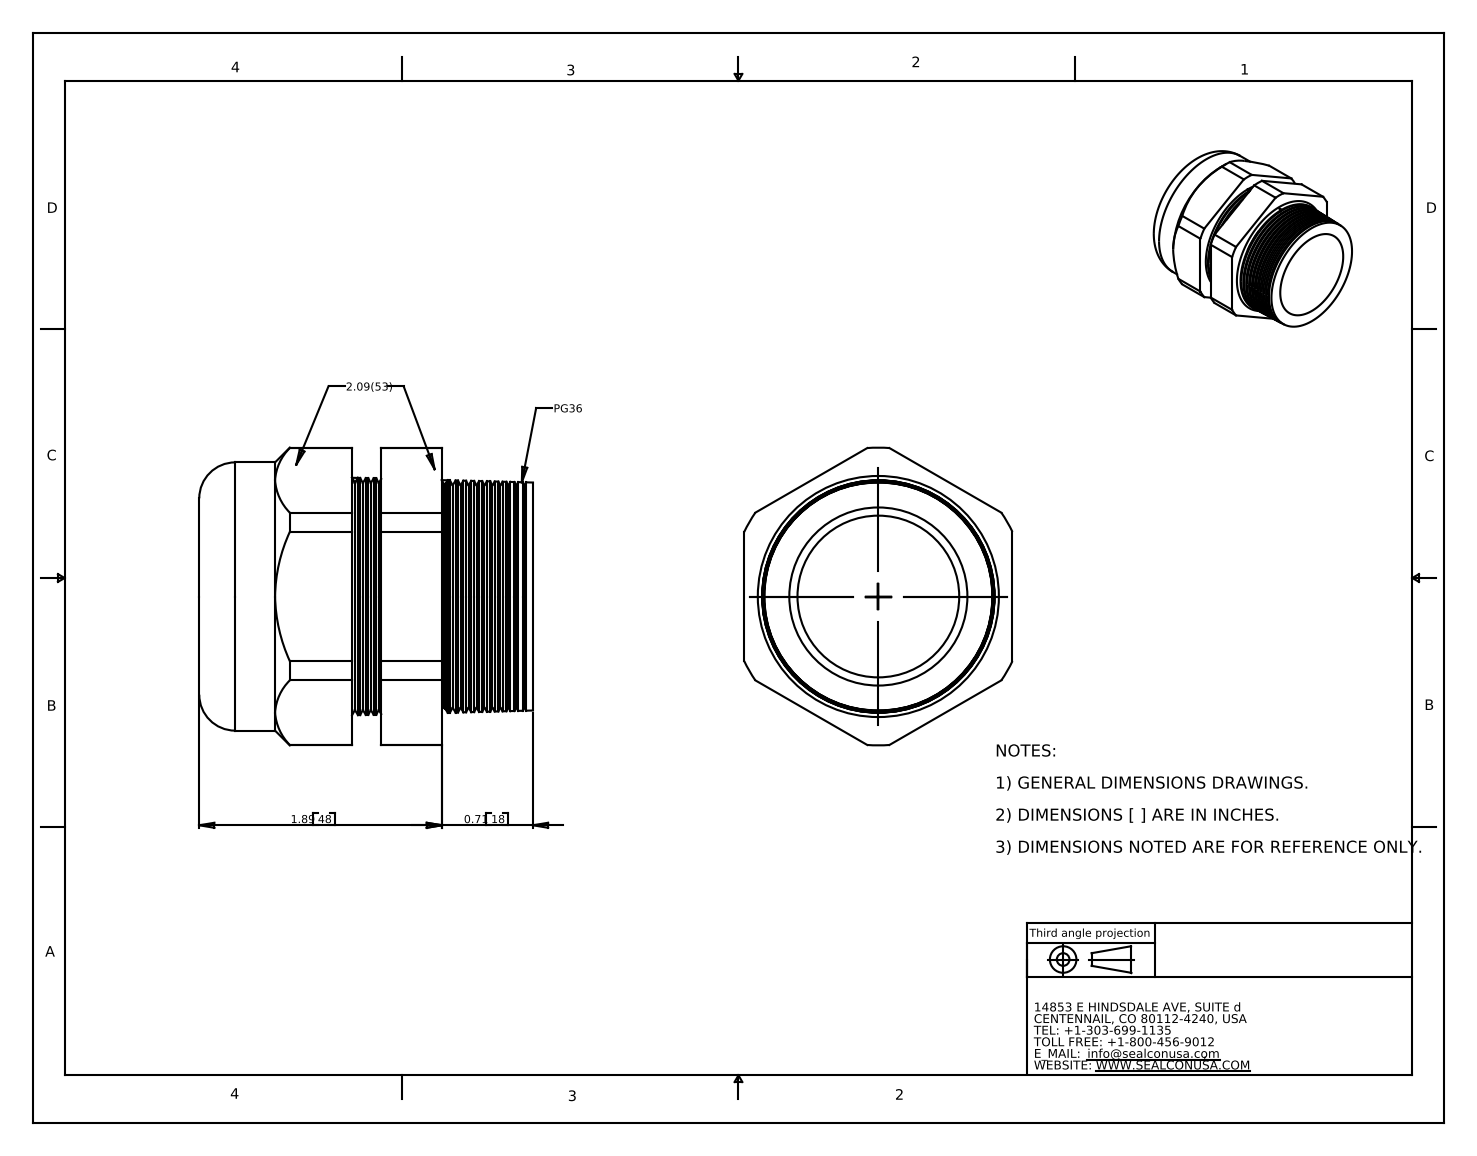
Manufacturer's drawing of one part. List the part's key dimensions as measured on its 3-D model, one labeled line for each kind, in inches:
Part name (STEP PRODUCT): CD36CA-BK
STEP written by: SolidWorks 2007 (CONFIG_CONTROL_DESIGN)
Units: inches
Bodies: 2 solids, 152 faces (20 planar, 22 cylindrical, 110 other)
Overall size (bounding box): 2.6 × 2.32 × 2.09
Volume: 4.838 in³ · Surface area: 42.13 in²
Round holes (diameter × count): ⌀1.26 ×1, ⌀1.387 ×1
Round bosses / shafts (diameter × count): ⌀2.09 ×1
Partial cylindrical surfaces — rounded edges, fillets, slot ends (radius × count): R1.16 ×1
Main face-to-face distances: 2.09, 0.227, 0.7, 0.472, 1.409, 1.182, 0.71, 0.6, 0.827, 1.3
